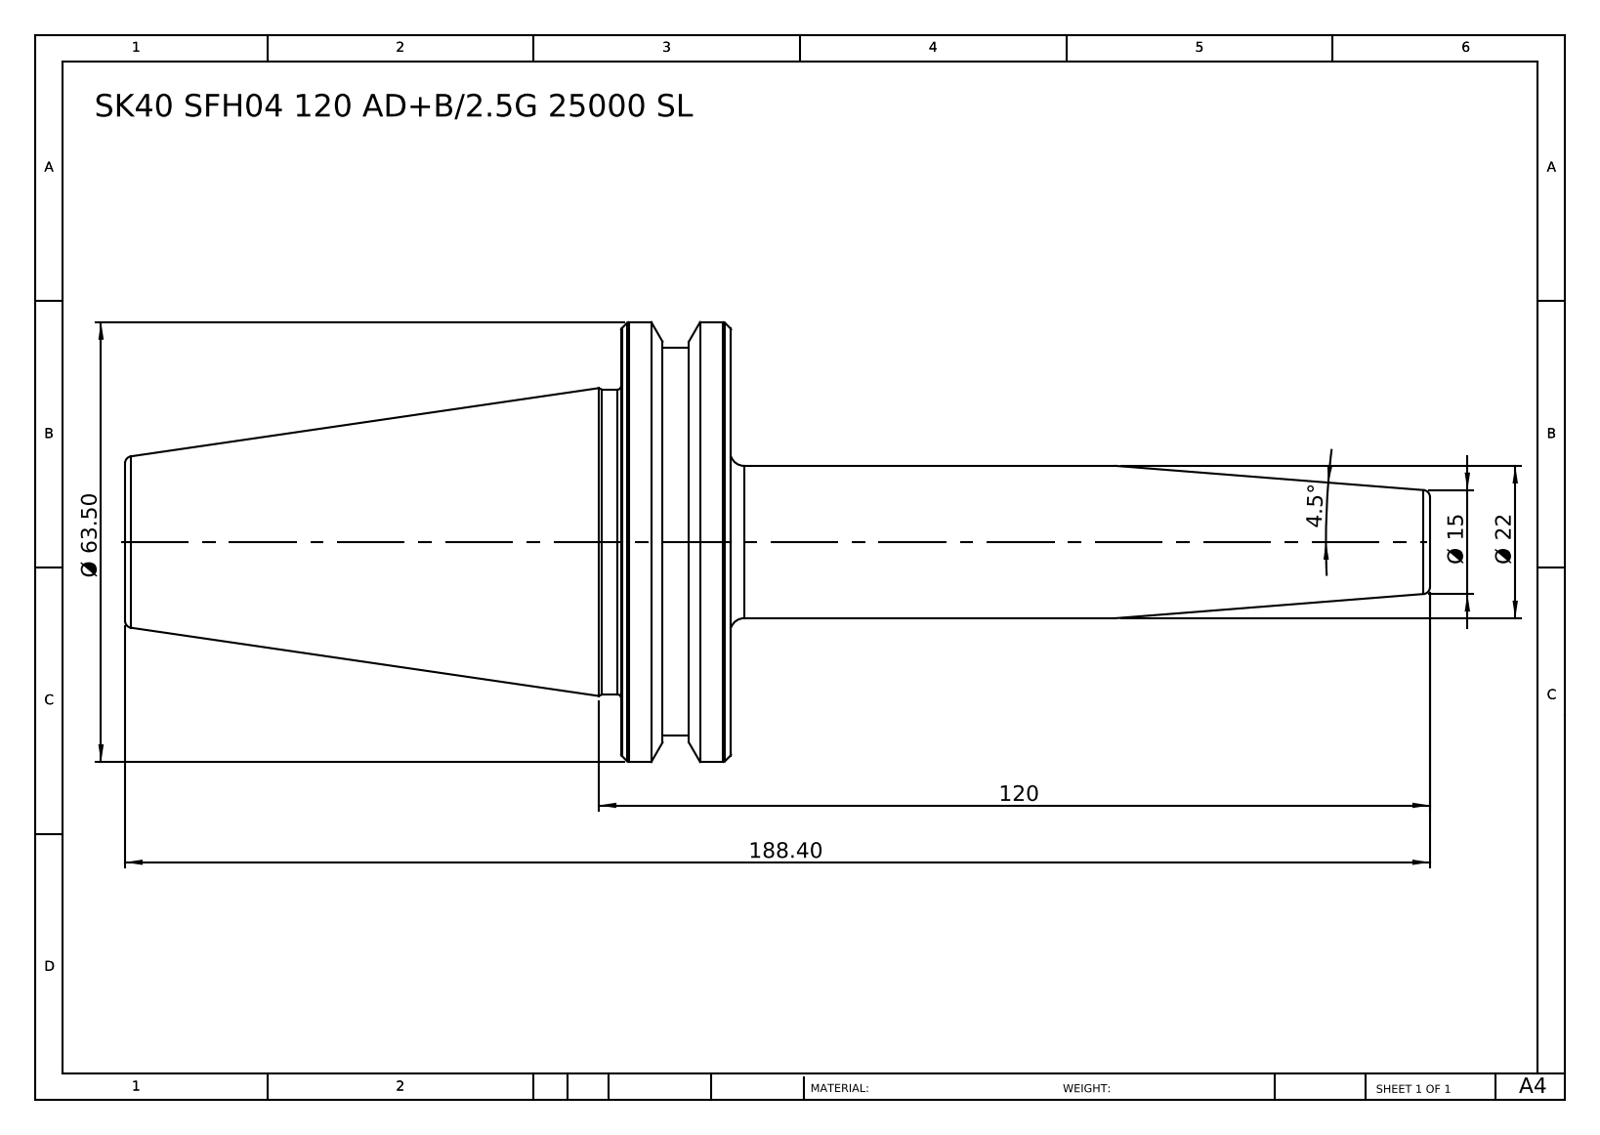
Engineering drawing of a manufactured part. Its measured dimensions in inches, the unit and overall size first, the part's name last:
Units: inches
Overall size (bounding box): 7.417 × 2.5 × 2.5
Round bosses / shafts (diameter × count): ⌀2.5 ×1, ⌀2.205 ×1, ⌀1.732 ×1, ⌀0.866 ×1
Main face-to-face distances: 0.626, 3.445, 2.819, 0.24, 0.386, 3.205, 0.39, 0.15, 0.236, 3.055
Volume: 9.184 in³ · Surface area: 35.84 in²
Bodies: 1 solid, 46 faces (6 planar, 10 cylindrical, 30 other)
Part name (STEP PRODUCT): SK40 SFH04 120 AD+B-2.5G 25000 SL
STEP written by: SolidWorks 2014 (CONFIG_CONTROL_DESIGN)
